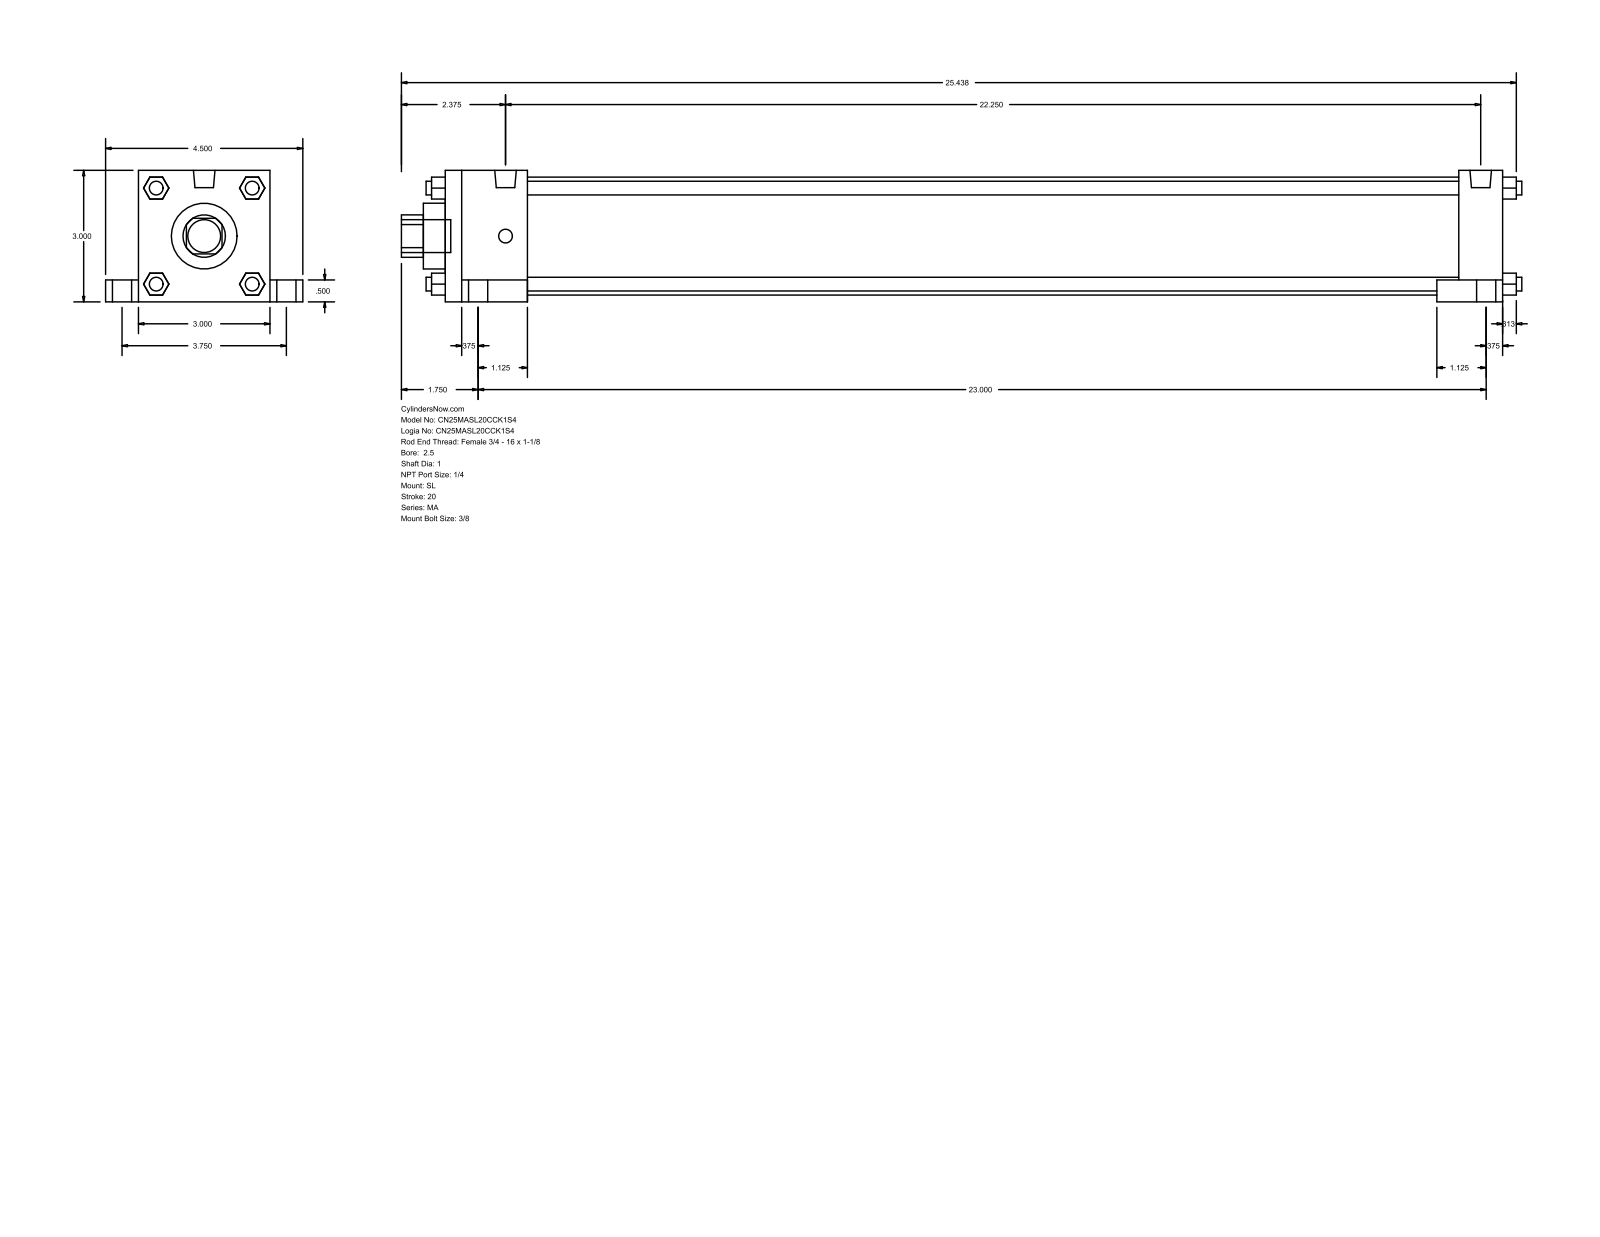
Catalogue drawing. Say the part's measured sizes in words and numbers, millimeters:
The part is named "MA_SL__0250_1". Its 3-D file was written by "GSSL Pune (CONFIG_CONTROL_DESIGN)". It is 0 solids with 148 faces: 112 planar, 36 cylindrical and 0 other. Overall it measures 649.29 by 114.3 by 76.2 millimeters. Round holes: 1 of diameter 25.4, 1 of diameter 38.1, 1 of diameter 68.33. Round bosses or shafts: 8 of diameter 7.94, 4 of diameter 17.46, 4 of diameter 11.11, 2 of diameter 12.49, 1 of diameter 19.05. Partial cylindrical surfaces (rounded edges, fillets, slot ends): 1 of radius 12.29. The main face-to-face distances are 76.2, 612.77, 12.7, 25.4, 47.63, 565.14, 587.37, 539.74, 19.05, 95.25.
